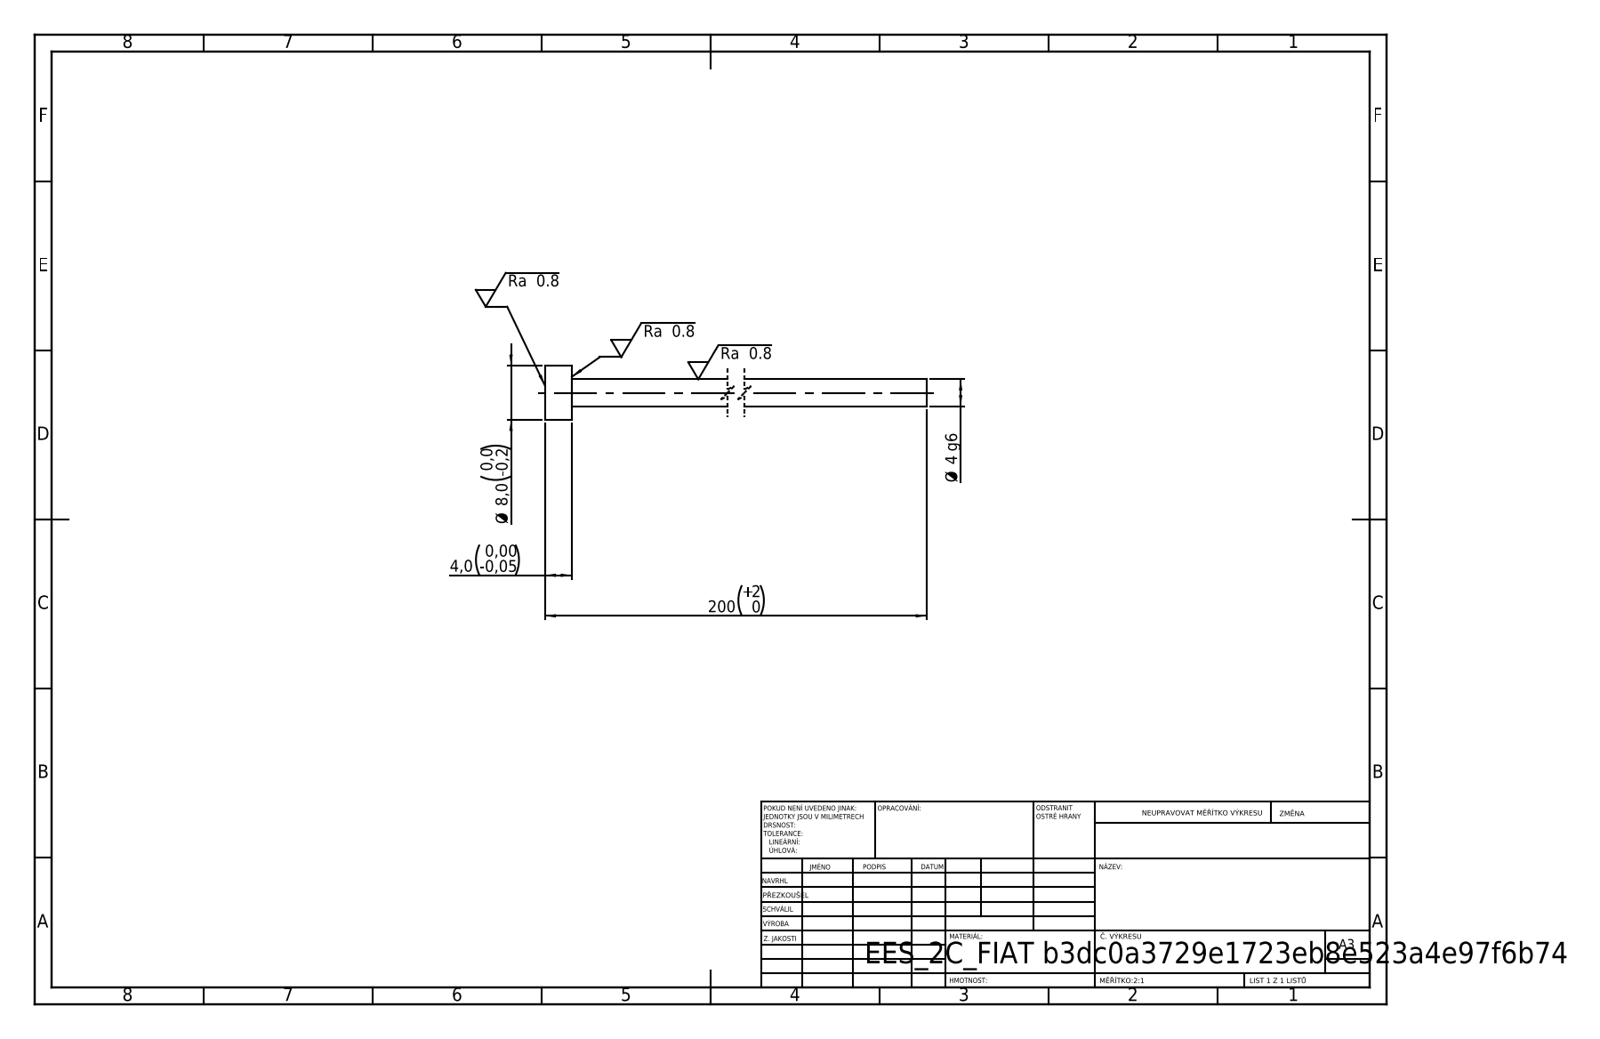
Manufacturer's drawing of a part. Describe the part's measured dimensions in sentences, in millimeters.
Its 3-D file was written by "SolidWorks 2019 (CONFIG_CONTROL_DESIGN)". It is 1 solid with 7 faces: 3 planar, 4 cylindrical and 0 other. Overall it measures 200 by 8 by 8 millimeters. Its volume is 2 664 cubic millimeters and its surface area 2 664 square millimeters. Round bosses or shafts: 1 of diameter 8, 1 of diameter 4. The main face-to-face distances are 4, 200, 196.
